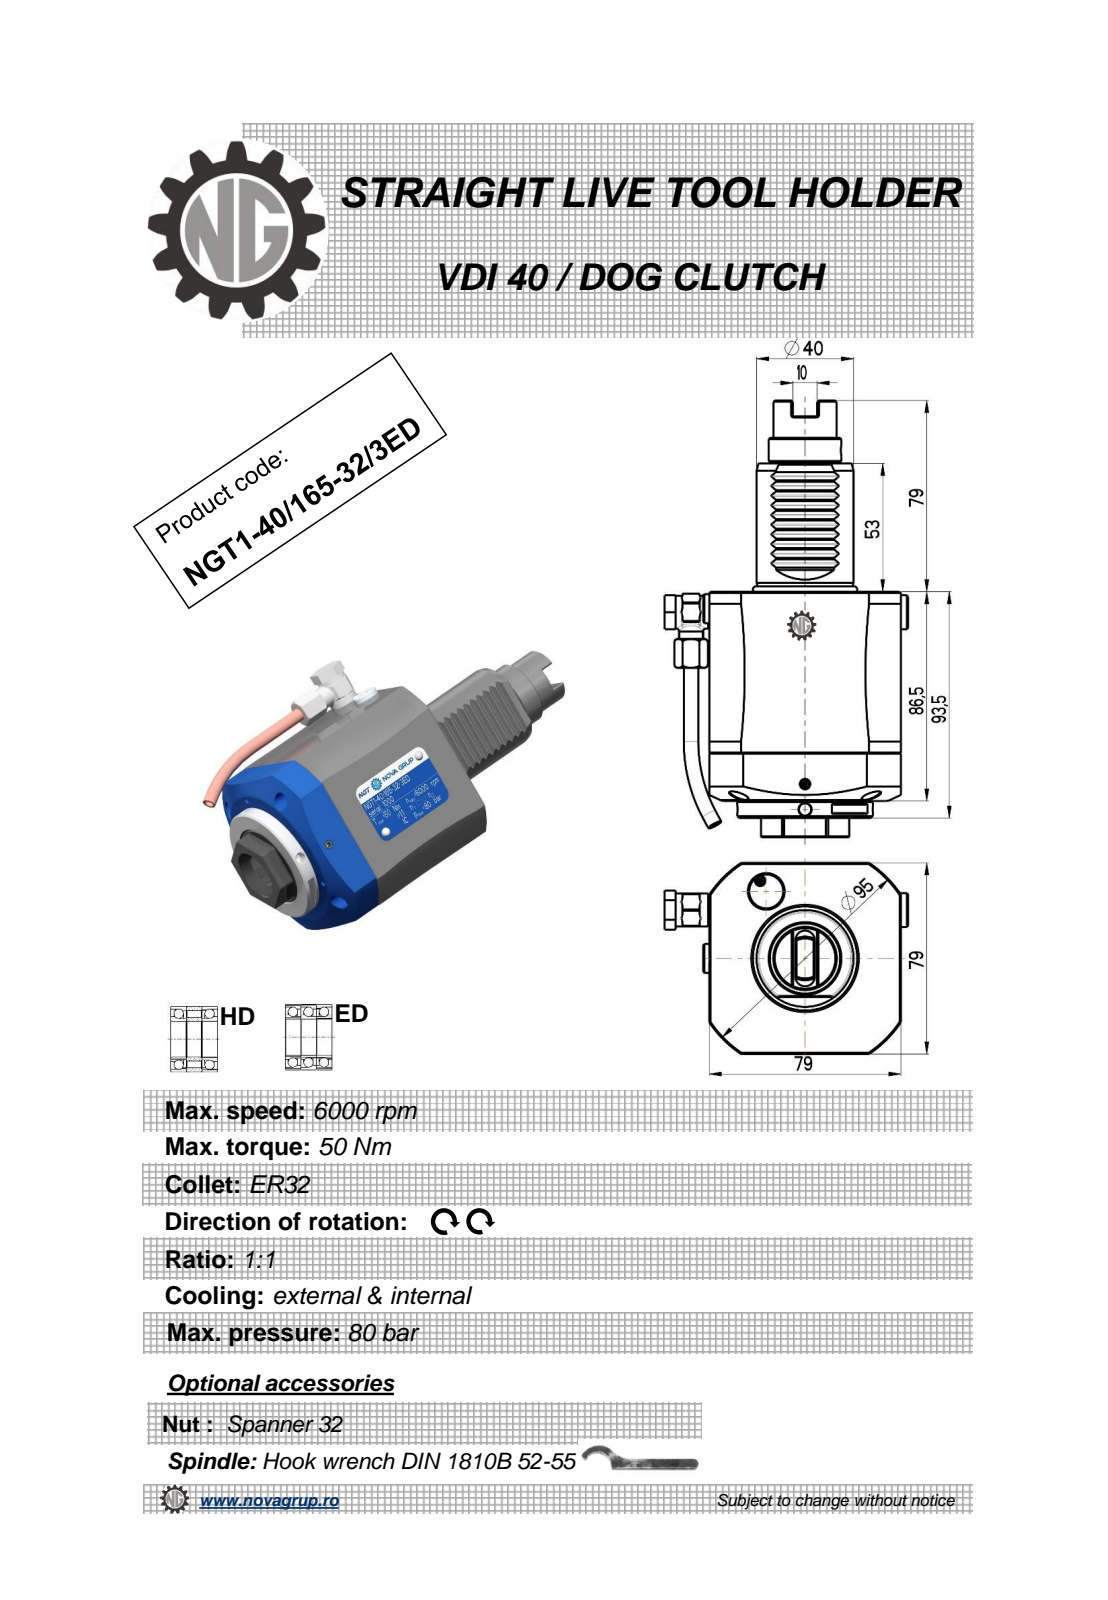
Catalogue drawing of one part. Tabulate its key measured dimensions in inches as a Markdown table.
| quantity | value |
| --- | --- |
| part name | NGT1_40_165_32_3HD |
| STEP written by | PRO/ENGINEER BY PARAMETRIC TECHNOLOGY CORPORATION, 2010280 (CONFIG_CONTROL_DESIGN) |
| units | inches |
| bodies | 2 solids, 388 faces (156 planar, 101 cylindrical, 131 other) |
| overall size | 7.106 × 3.953 × 3.11 |
| volume | 36.79 in³ |
| surface area | 85.54 in² |
| round holes (diameter × count) | 0.157 × 3, 0.197 × 2, 0.118 × 1, 0.236 × 1, 0.244 × 1, 0.354 × 1, 0.394 × 1, 0.433 × 1, 0.906 × 1 |
| round bosses / shafts (diameter × count) | 2.205 × 1, 1.575 × 1, 1.181 × 1, 1.024 × 1, 0.551 × 1, 0.535 × 1, 0.512 × 1, 0.472 × 1 |
| partial cylindrical surfaces (radius × count) | 0.012 × 10, 0.016 × 6, 0.02 × 6, 0.303 × 1, 1.85 × 1, 1.87 × 1 |
| main face-to-face distances | 3.11, 3.406, 0.276, 3.681, 0.111, 5.492, 5.768, 2.087, 0.334, 0.557 |
| hole center spacings | 0.016, 2.011, 2.026, 3.304 |
